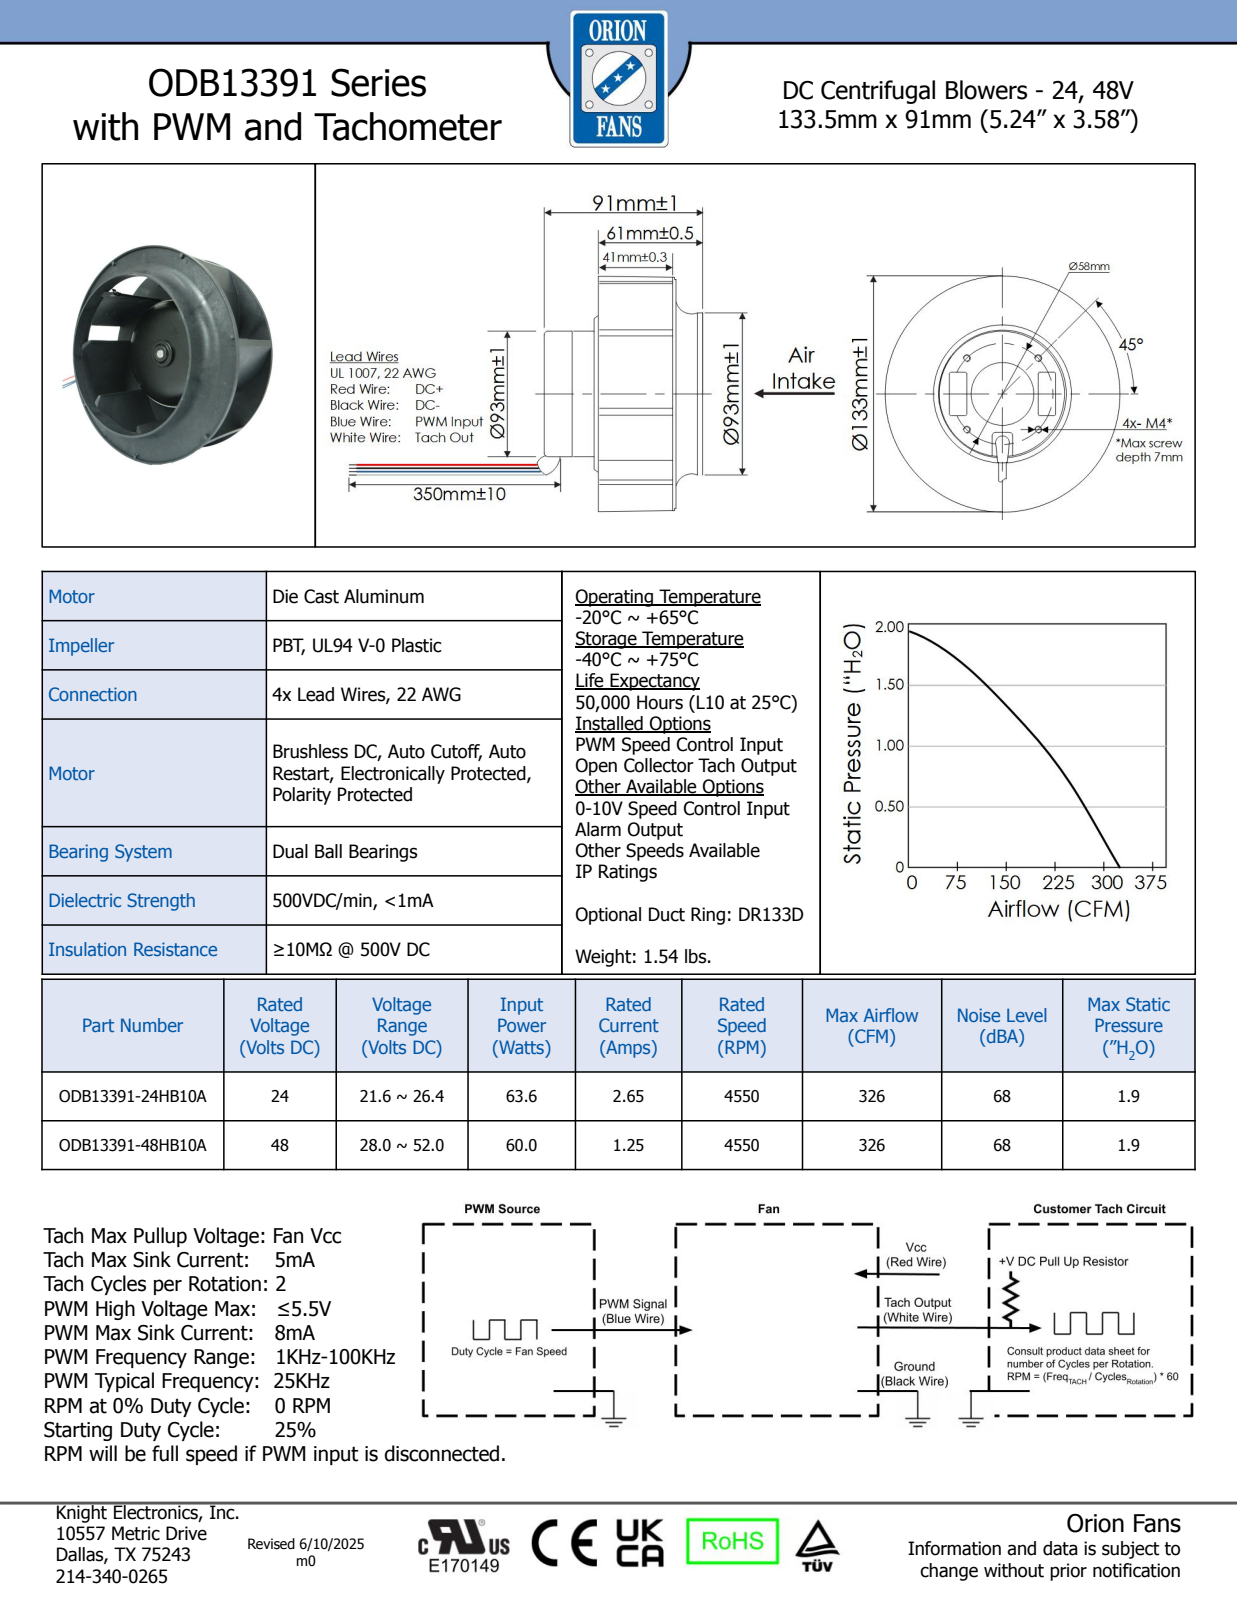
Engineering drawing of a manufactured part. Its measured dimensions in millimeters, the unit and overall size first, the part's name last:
Units: millimetres
Overall size (bounding box): 133.5 × 133.5 × 91
Round holes (diameter × count): ⌀3.5 ×4, ⌀2.5 ×3, ⌀8 ×1, ⌀17 ×1, ⌀19 ×1, ⌀19.5 ×1, ⌀36 ×1, ⌀68 ×1, ⌀70 ×1, ⌀76.6 ×1, ⌀93.5 ×1, ⌀130.9 ×1
Round bosses / shafts (diameter × count): ⌀0.7 ×7, ⌀133.5 ×1, ⌀96 ×1, ⌀84.5 ×1, ⌀72 ×1, ⌀25 ×1, ⌀23 ×1, ⌀14 ×1
Partial cylindrical surfaces — rounded edges, fillets, slot ends (radius × count): R0.5 ×24, R0.95 ×7, R1.2 ×7, R62.74 ×7, R64.64 ×7, R3.5 ×2
Main face-to-face distances: 1.6, 44, 22.1, 42.6, 41, 42.4, 1.4, 2, 20.5, 22.5
Hole centre spacings: 29.01, 41.02, 24, 12.47, 20.8, 21.83, 28.79, 30
Volume: 110 725 mm³ · Surface area: 124 663 mm²
Bodies: 4 solids, 751 faces (284 planar, 152 cylindrical, 315 other)
Part name (STEP PRODUCT): ODB13391
STEP written by: SolidWorks 2018 (CONFIG_CONTROL_DESIGN)
